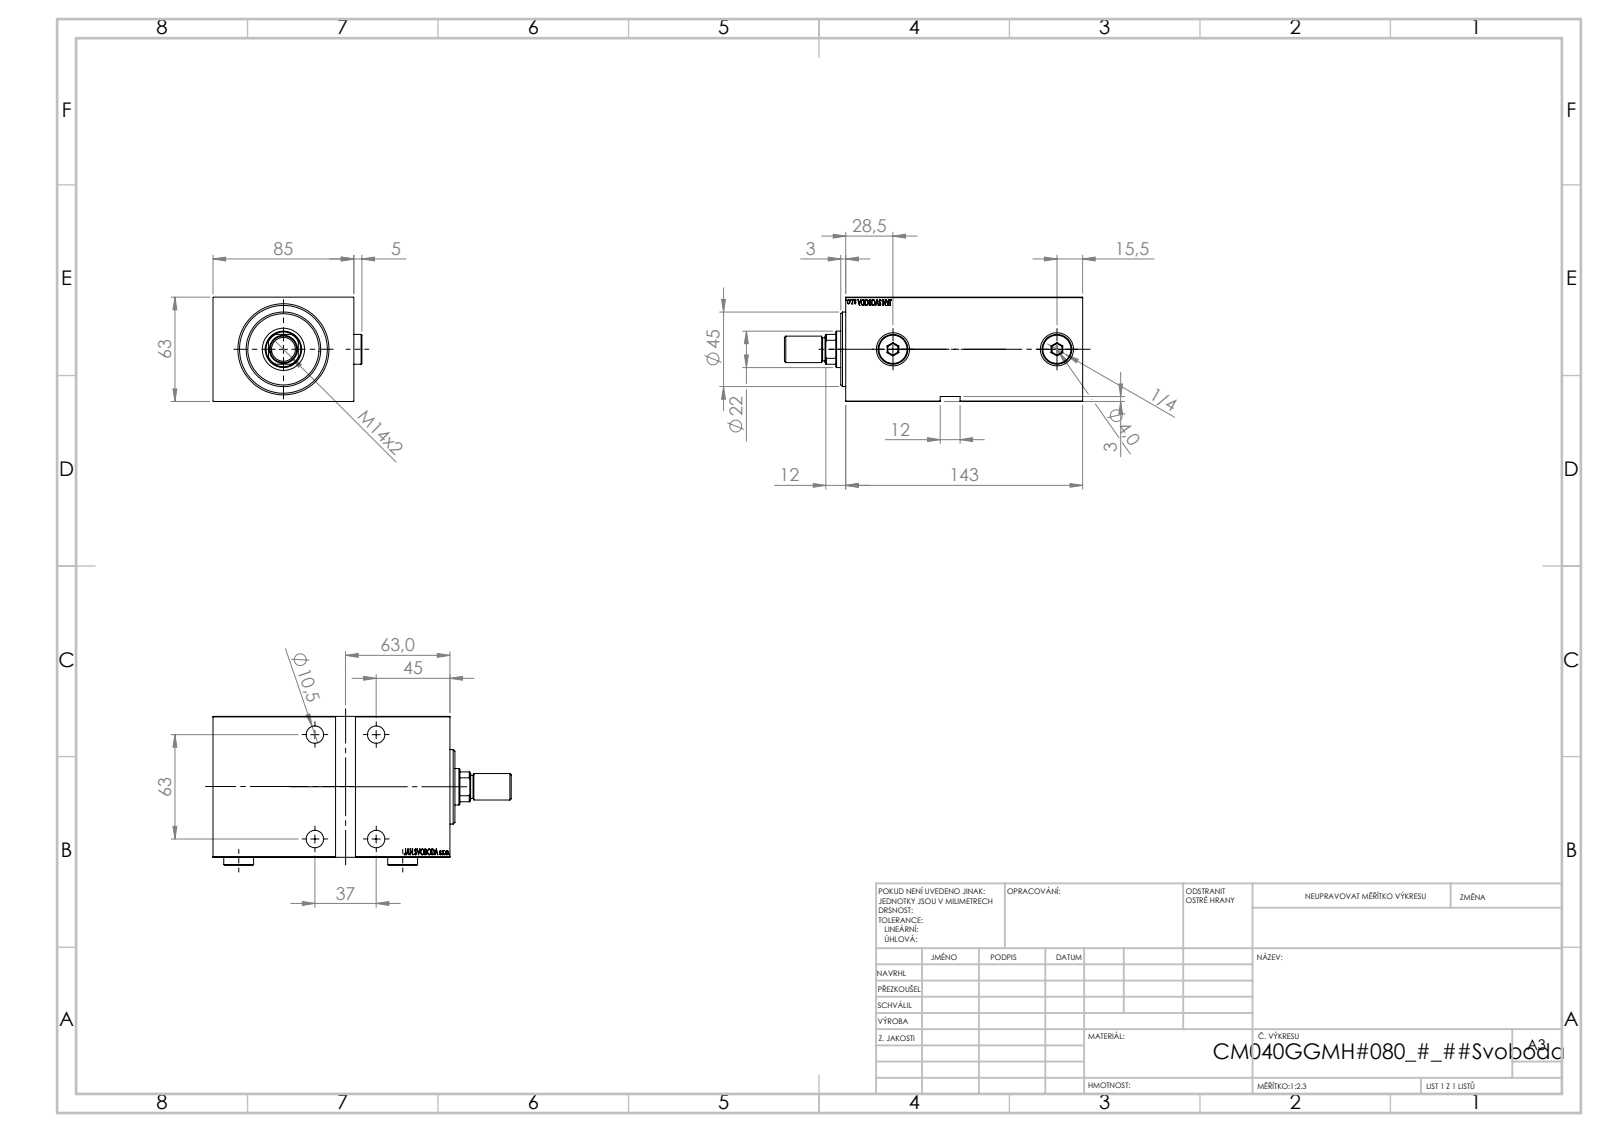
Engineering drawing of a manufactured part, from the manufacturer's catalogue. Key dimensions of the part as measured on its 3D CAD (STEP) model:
Part name (STEP PRODUCT): V450CM_G_Body; V450CM_VC_G; V450CM_MALE_METRIC; V450CM_G_VCP (+1 more)
STEP written by: SolidWorks 2019 (CONFIG_CONTROL_DESIGN)
Units: millimetres
Bodies: 6 solids, 913 faces (447 planar, 62 cylindrical, 404 other)
Overall size (bounding box): 180 × 89.9 × 63
Volume: 664 885 mm³ · Surface area: 105 490 mm²
Round holes (diameter × count): ⌀10.5 ×4, ⌀16.5 ×4, ⌀4 ×2, ⌀13.16 ×2, ⌀20 ×2, ⌀12.5 ×1, ⌀22 ×1, ⌀25.5 ×1, ⌀40 ×1, ⌀42 ×1, ⌀53 ×1
Round bosses / shafts (diameter × count): ⌀18 ×2, ⌀45 ×1, ⌀27 ×1, ⌀16 ×1, ⌀14 ×1
Partial cylindrical surfaces — rounded edges, fillets, slot ends (radius × count): R10.5 ×1
Main face-to-face distances: 63, 85, 143, 12, 131, 5, 138, 126, 3, 60
Hole centre spacings: 37, 63, 73.06, 99
